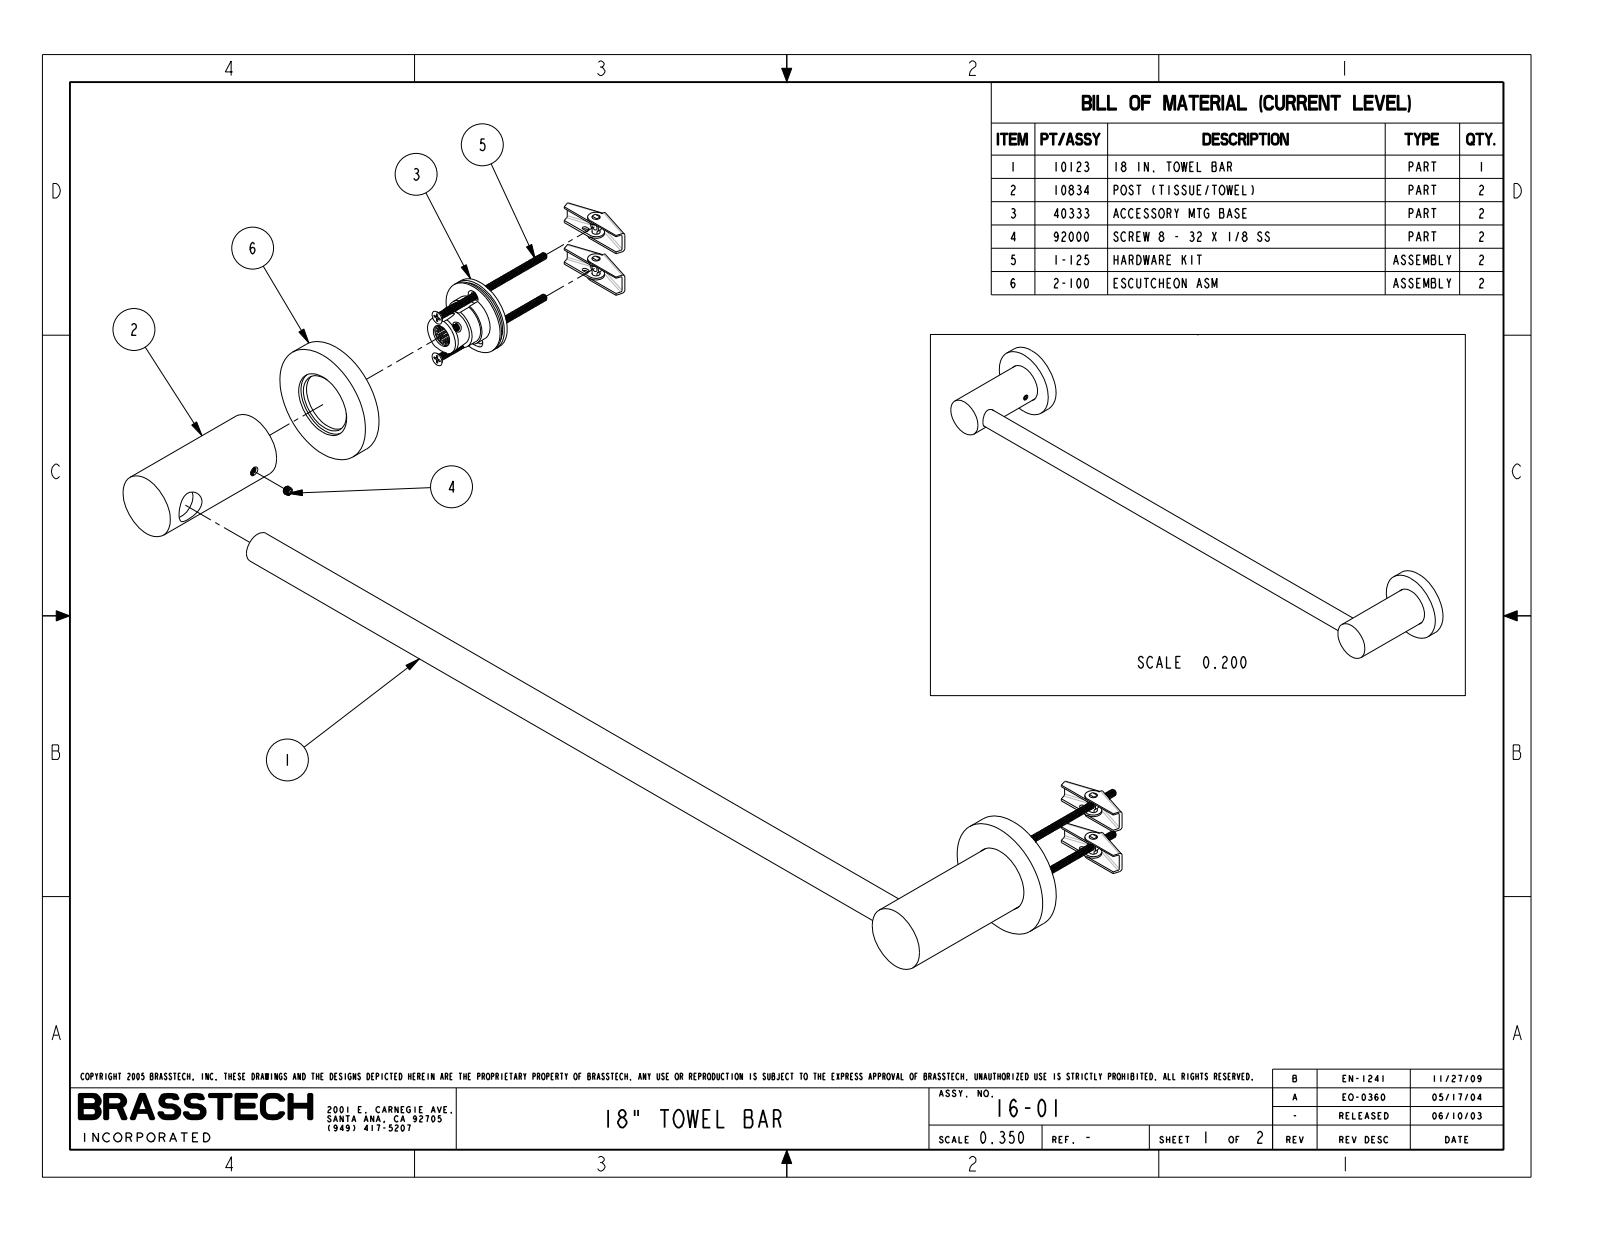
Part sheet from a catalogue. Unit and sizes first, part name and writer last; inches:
Units: inches
Overall size (bounding box): 21.188 × 3.267 × 2.375
Round bosses / shafts (diameter × count): ⌀2.375 ×2, ⌀1.313 ×2, ⌀0.625 ×1
Main face-to-face distances: 0.375, 3.266, 2.891
Bodies: 0 solids, 24 faces (6 planar, 10 cylindrical, 8 other)
Part name (STEP PRODUCT): 16-01_WEB
STEP written by: PRO/ENGINEER BY PARAMETRIC TECHNOLOGY CORPORATION, 2009300 (CONFIG_CONTROL_DESIGN)
